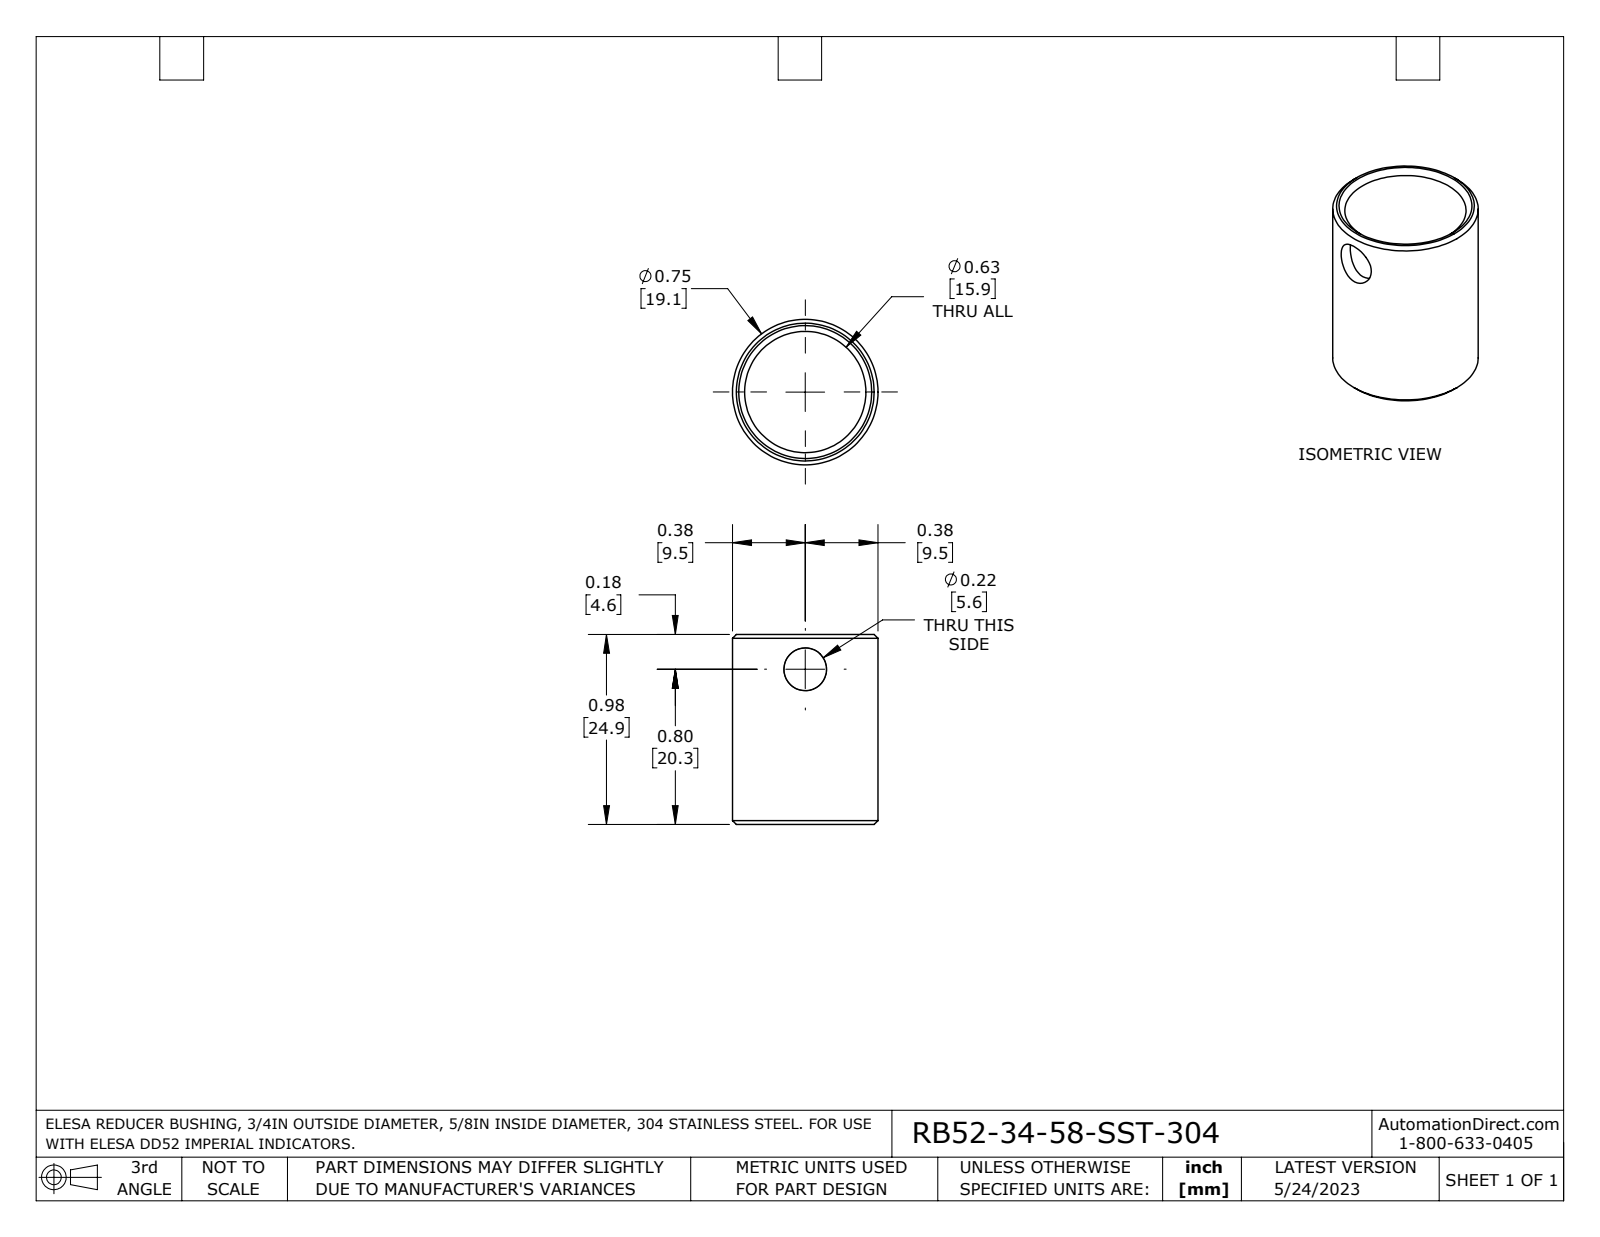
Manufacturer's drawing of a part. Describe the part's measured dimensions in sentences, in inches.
The part is named "RB52-34-58-SST-304". Its 3-D file was written by "SolidWorks 2021 (AUTOMOTIVE_DESIGN)". It is 1 solid with 9 faces: 2 planar, 2 cylindrical and 5 other. Overall it measures 0.98 by 0.75 by 0.75 inches. Its volume is 0.127 cubic inches and its surface area 4.348 square inches. Round holes: 1 of diameter 0.625. Round bosses or shafts: 1 of diameter 0.75. The main face-to-face distances are 0.98.
